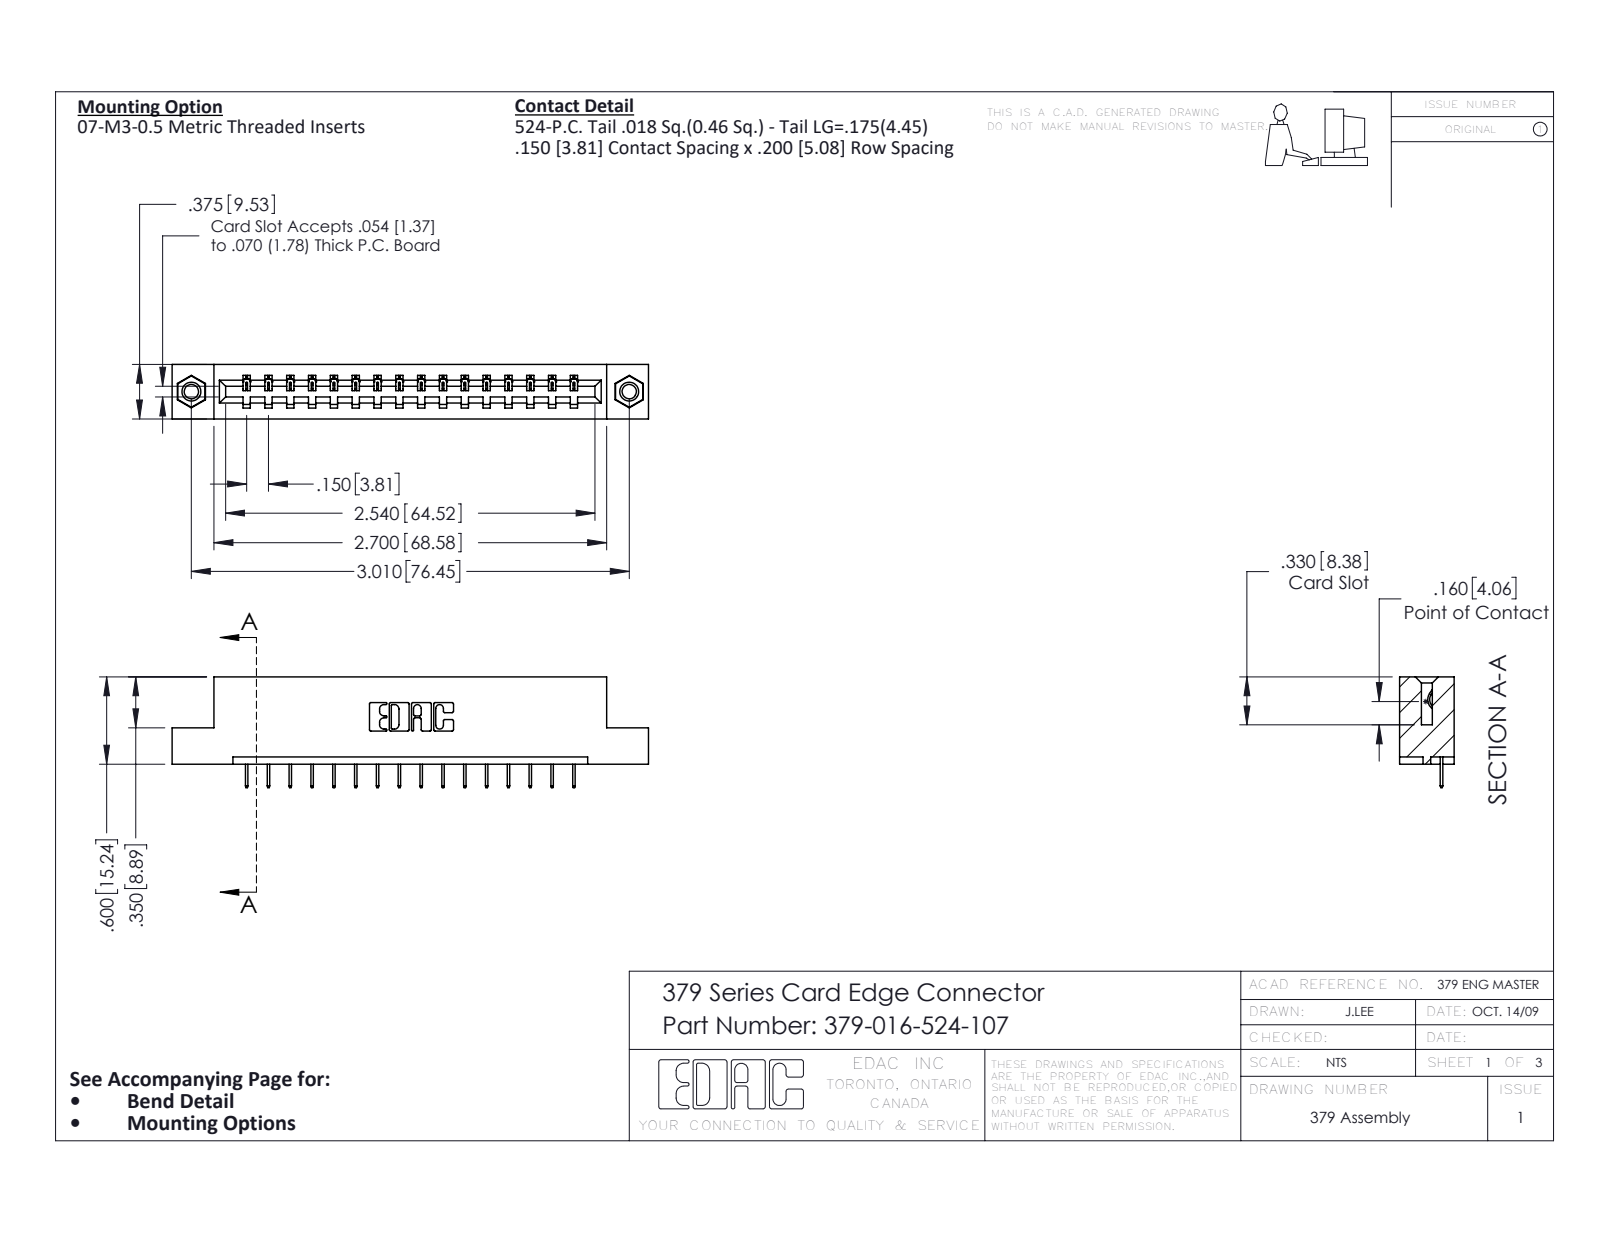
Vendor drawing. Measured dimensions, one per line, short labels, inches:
name: 379-016-524-107; 379 Part_Flush - .156 Dia - TI; 345-250-001_345-250-005-103; 345-292-001_345-293-124
written by: SolidWorks 2020 (CONFIG_CONTROL_DESIGN)
unit: in
bodies: 19 solids, 1166 faces (870 planar, 280 cylindrical, 16 other)
size: 3.275 × 0.762 × 0.375
volume: 0.51 in³; area: 12.76 in²
holes: 2× ⌀0.098, 2× ⌀0.125, 2× ⌀0.156
bosses: 2× ⌀0.155
rounds: 32× R0.006, 22× R0.01, 6× R0.007, 6× R0.031, 3× R0.026, 1× R0.014, 1× R0.022, 1× R0.024
face distances: 0.3, 0.375, 0.075, 0.6, 0.15, 0.225, 0.45, 0.75, 0.2, 0.9
hole spacings: 3.01
